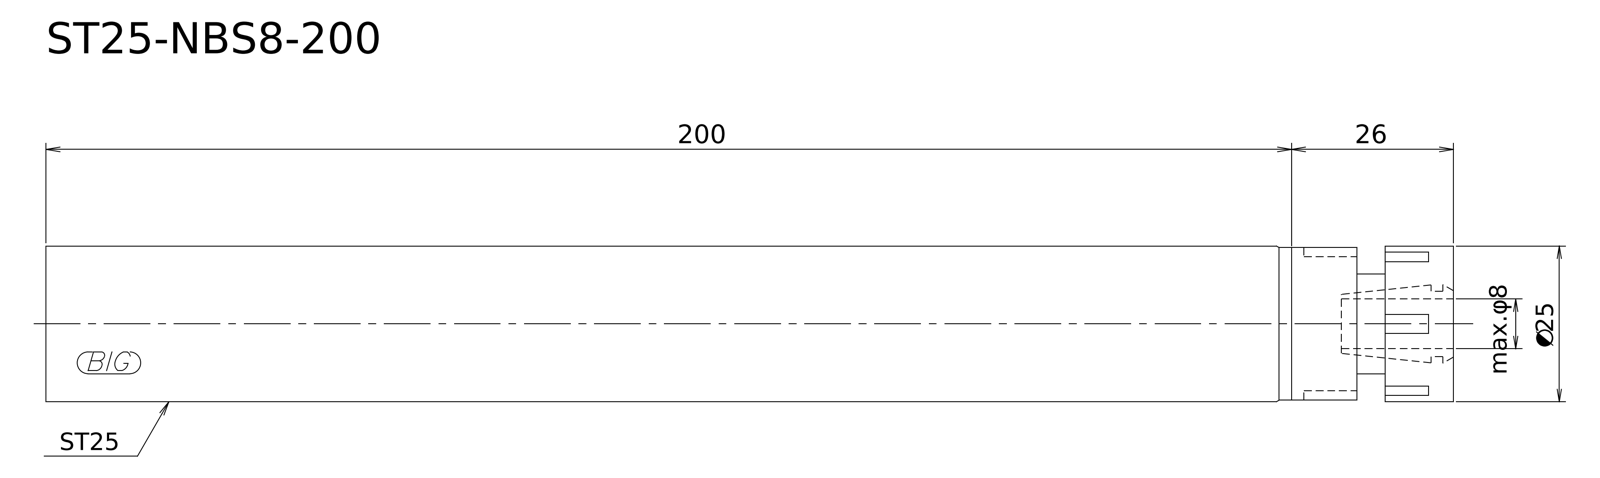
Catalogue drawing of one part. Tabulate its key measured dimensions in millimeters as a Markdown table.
| quantity | value |
| --- | --- |
| STEP written by | Kubotek KeyCreator V8.5.1 (14335) (CONFIG_CONTROL_DESIGN) |
| units | millimeters |
| bodies | 1 solid, 9 faces (5 planar, 4 cylindrical, 0 other) |
| overall size | 226 × 25 × 25 |
| volume | 109 384 mm³ |
| surface area | 19 164 mm² |
| round bosses / shafts (diameter × count) | 25 × 1, 24.5 × 1, 16 × 1 |
| main face-to-face distances | 226, 11, 215, 15.5, 4.5, 210.5, 28.35, 17.35, 12.85, 197.65 |
